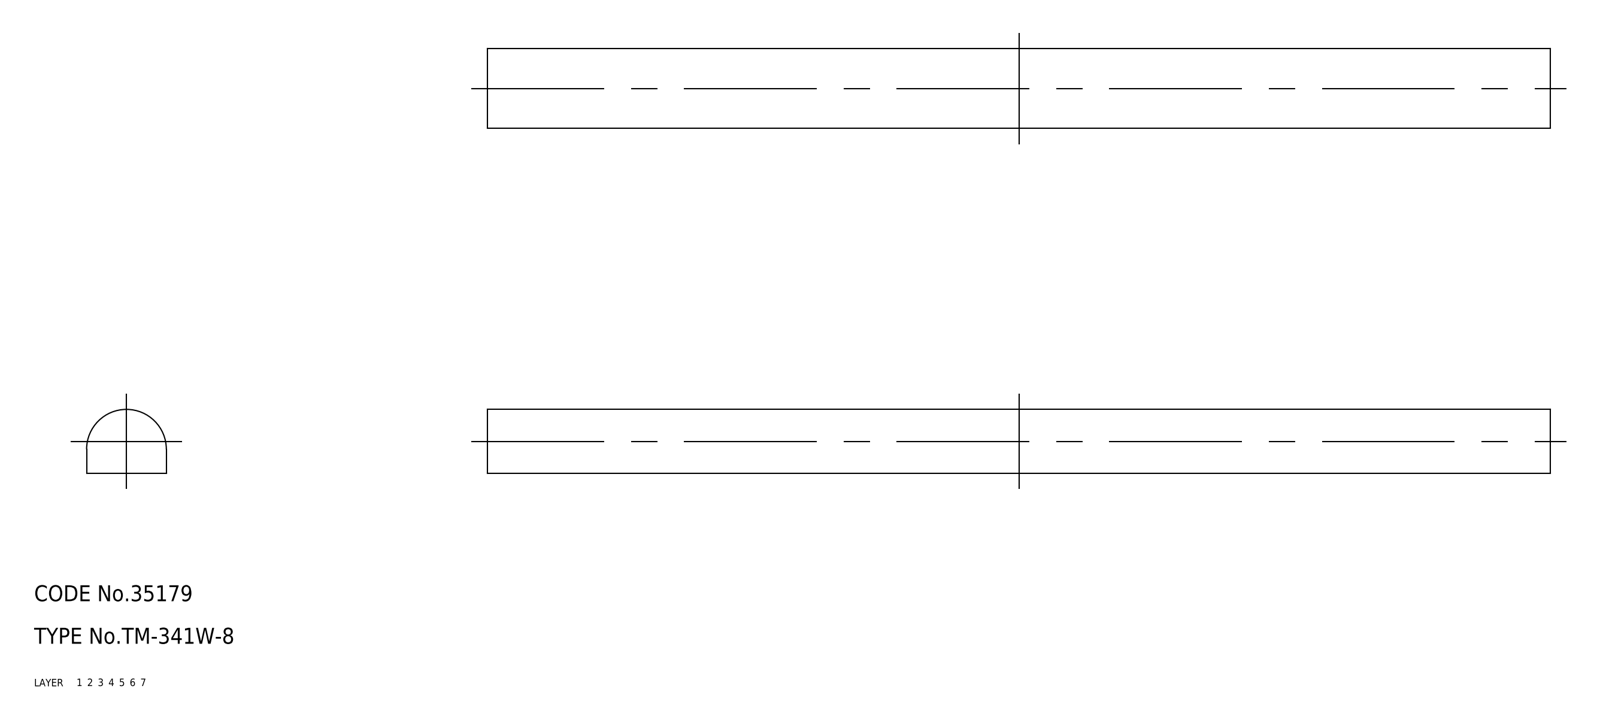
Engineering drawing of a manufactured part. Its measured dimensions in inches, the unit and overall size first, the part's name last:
Units: inches
Overall size (bounding box): 7.874 × 0.591 × 0.472
Partial cylindrical surfaces — rounded edges, fillets, slot ends (radius × count): R0.295 ×1
Main face-to-face distances: 0.591, 7.874
Volume: 1.902 in³ · Surface area: 15.23 in²
Bodies: 1 solid, 6 faces (5 planar, 1 cylindrical, 0 other)
Part name (STEP PRODUCT): rubber foam; TM_341W_8
STEP written by: SolidWorks 2015 (AUTOMOTIVE_DESIGN)
